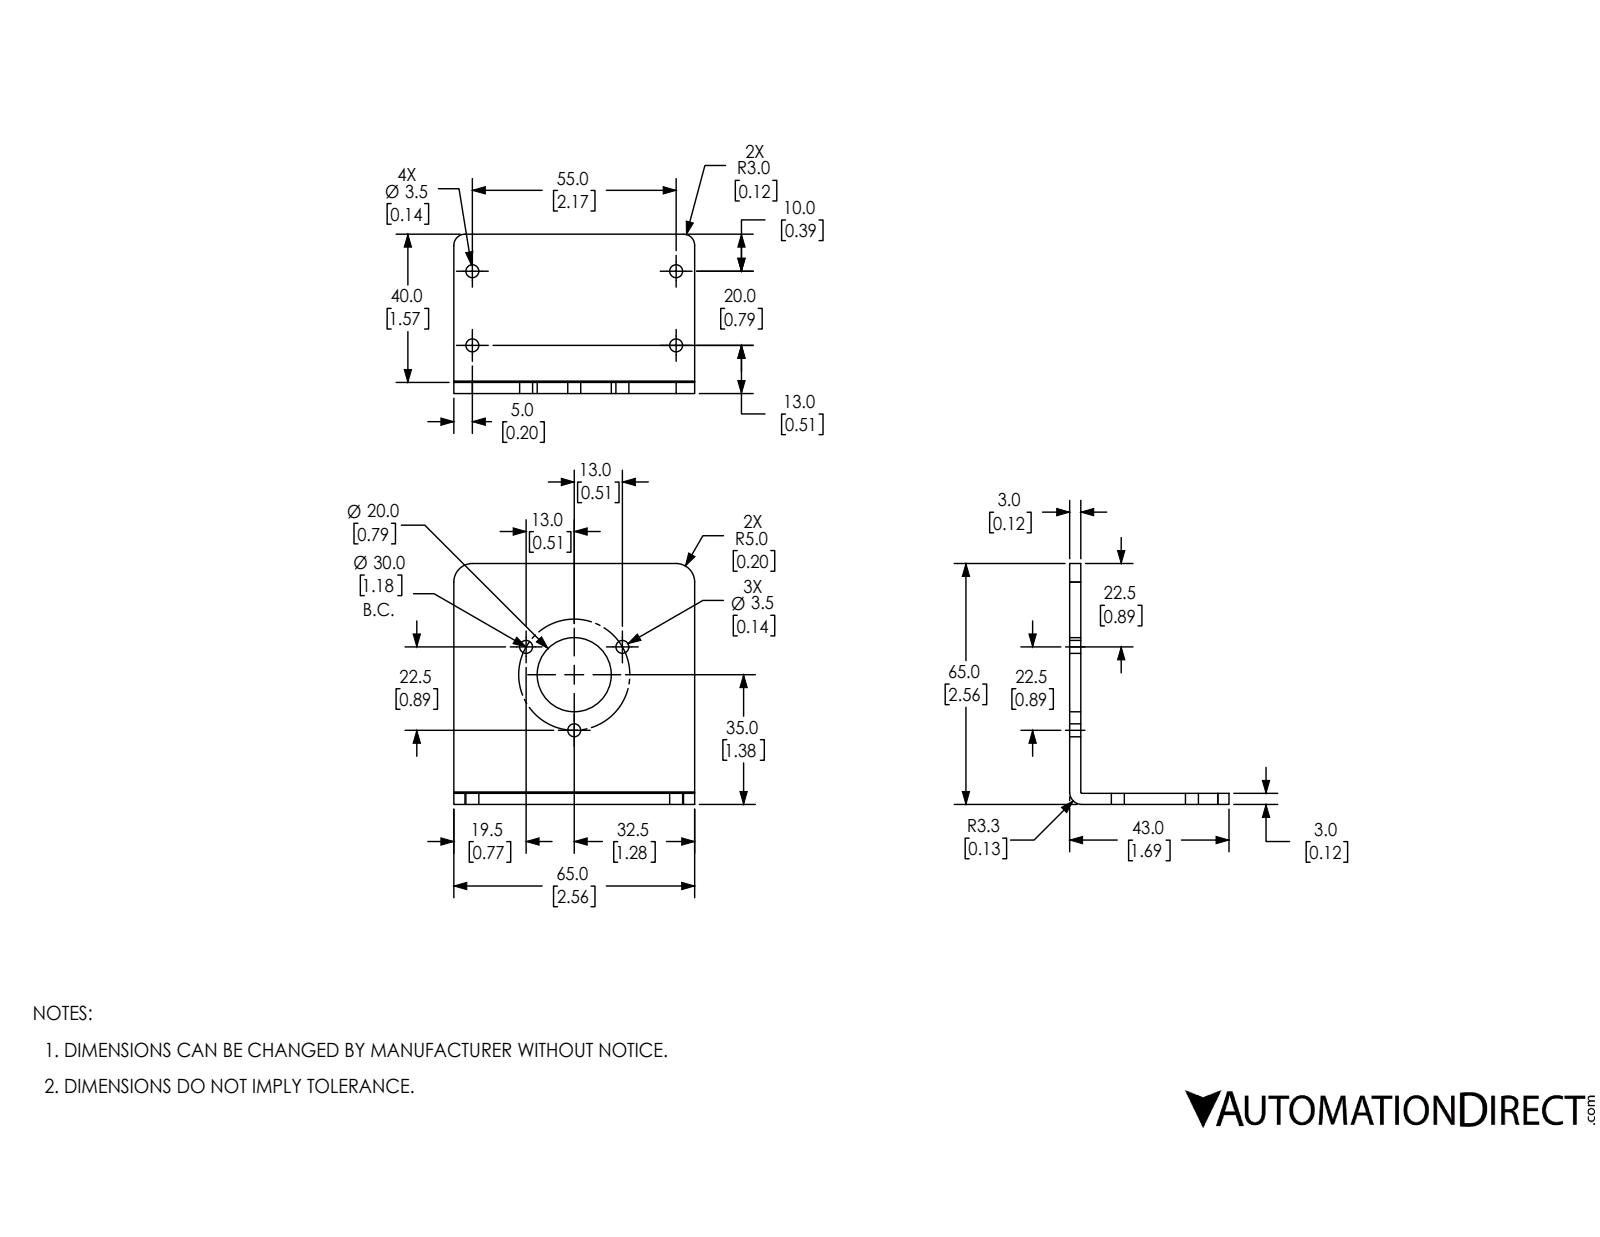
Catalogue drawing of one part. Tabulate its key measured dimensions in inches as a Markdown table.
| quantity | value |
| --- | --- |
| part name | TRD-SR-035 |
| STEP written by | SolidWorks 2017 (AUTOMOTIVE_DESIGN) |
| units | inches |
| bodies | 1 solid, 30 faces (8 planar, 22 cylindrical, 0 other) |
| overall size | 2.559 × 2.559 × 1.693 |
| volume | 1.168 in³ |
| surface area | 21.97 in² |
| round holes (diameter × count) | 0.138 × 7, 0.787 × 1 |
| partial cylindrical surfaces (radius × count) | 0.118 × 2, 0.197 × 2, 0.012 × 1, 0.13 × 1 |
| main face-to-face distances | 0.118, 2.559, 1.575, 1.693, 2.441 |
| hole center spacings | 0.591, 1.023, 0.787, 2.165, 2.304 |
